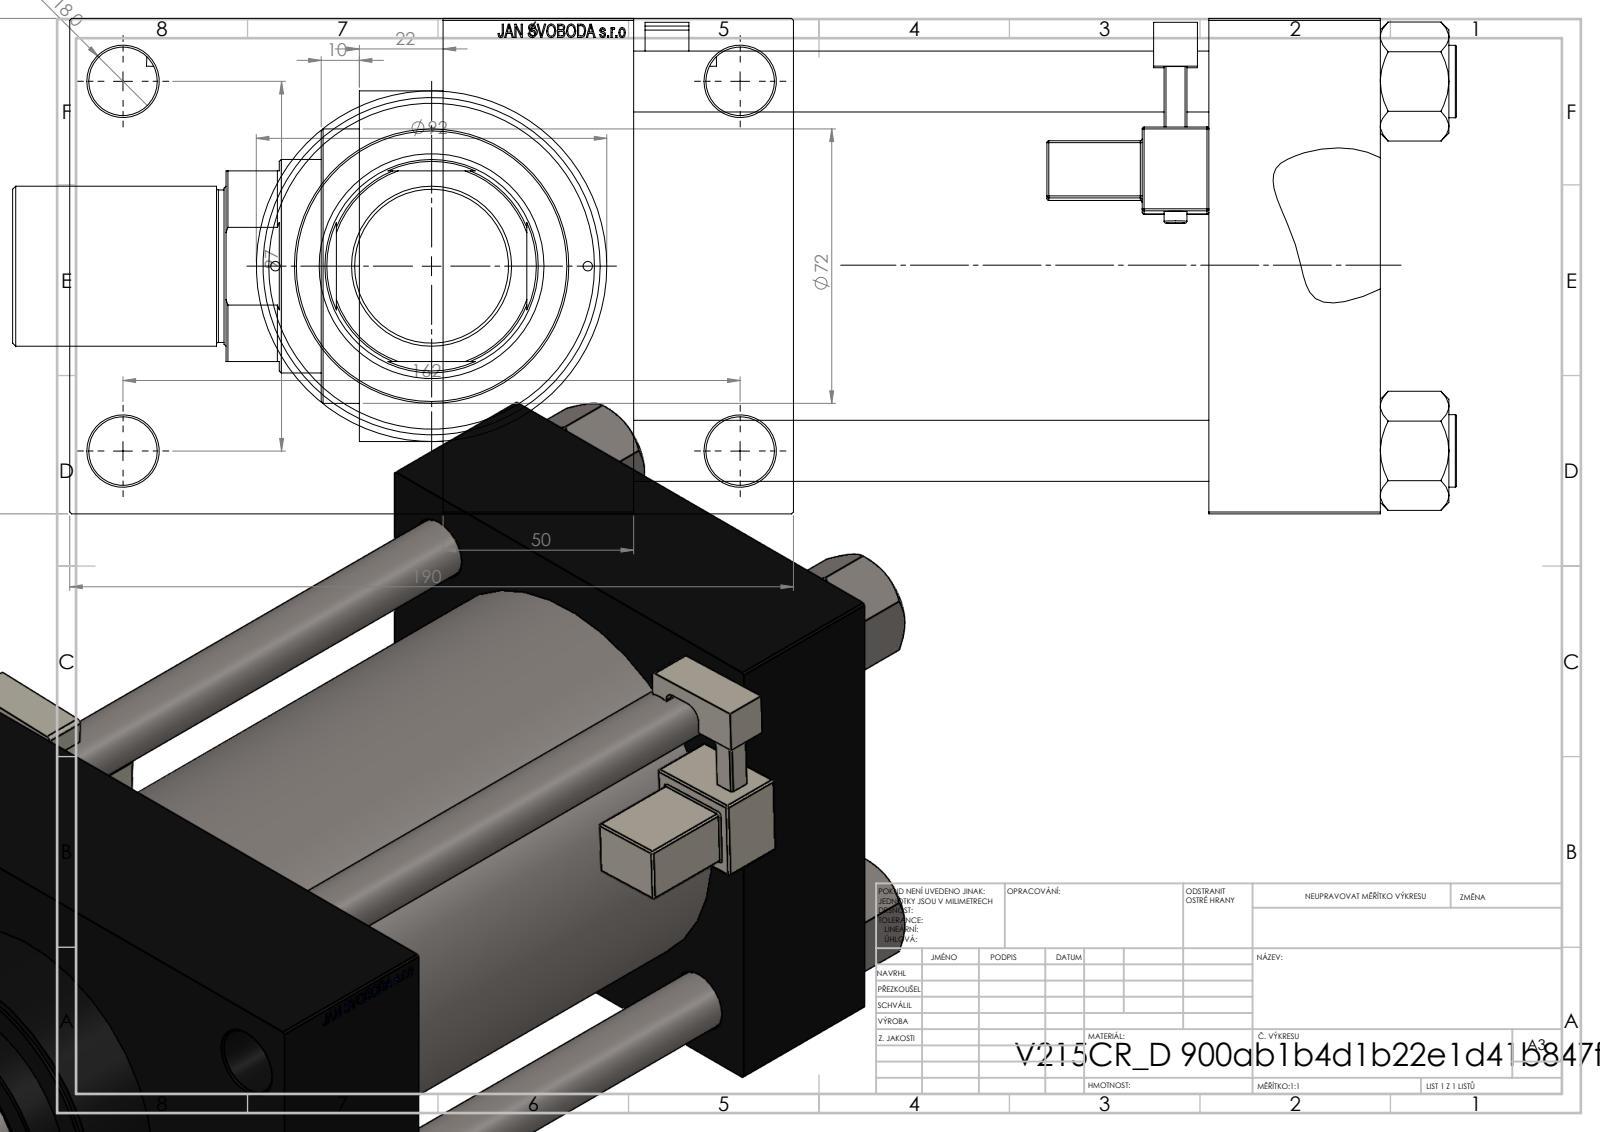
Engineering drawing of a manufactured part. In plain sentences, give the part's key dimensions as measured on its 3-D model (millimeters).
The part is named "NUT_M5_D; V215CR_MSU; V215CR_VCP_D; V215CR_D_Body (+3 more)". Its 3-D file was written by "SolidWorks 2019 (CONFIG_CONTROL_DESIGN)". It is 14 solids with 1327 faces: 609 planar, 156 cylindrical and 562 other. Overall it measures 379 by 190 by 130 millimeters. Its volume is 3 085 000 cubic millimeters and its surface area 466 870 square millimeters. Round holes: 4 of diameter 16, 4 of diameter 18, 2 of diameter 2.5, 2 of diameter 7, 2 of diameter 26.44, 2 of diameter 35, 1 of diameter 40.5, 1 of diameter 56, 1 of diameter 59, 1 of diameter 76, 1 of diameter 85.5, 1 of diameter 100. Round bosses or shafts: 4 of diameter 19, 2 of diameter 6, 1 of diameter 106, 1 of diameter 92, 1 of diameter 72, 1 of diameter 42, 1 of diameter 40. Partial cylindrical surfaces (rounded edges, fillets, slot ends): 48 of radius 0.5, 2 of radius 1, 2 of radius 2.5, 2 of radius 4, 1 of radius 27. The main face-to-face distances are 130, 151, 50, 45, 196, 246, 201, 30, 160, 150. The hole center spacings are 32.55, 49.02, 62.87, 68.52, 94.41, 96.9, 101.73, 102.27.
